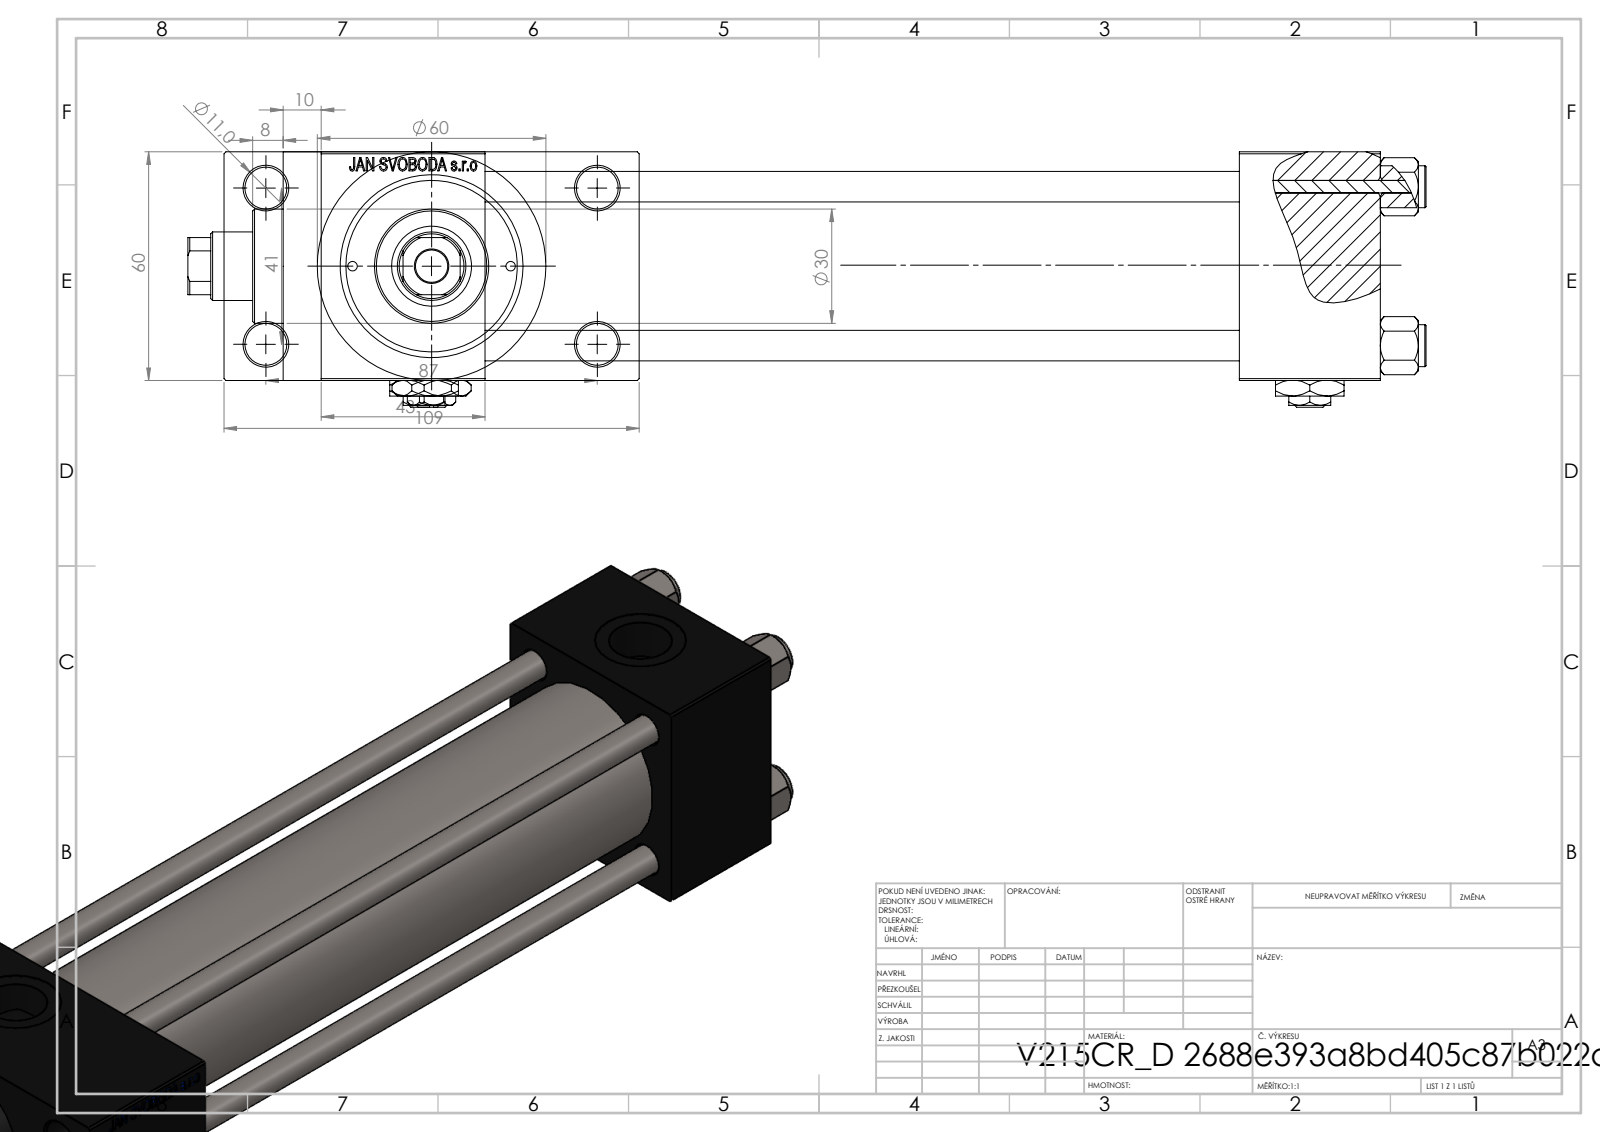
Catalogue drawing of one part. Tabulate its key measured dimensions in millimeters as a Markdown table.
| quantity | value |
| --- | --- |
| part name | V215CR_VCP_D; V215CR_D_Body; V215_VC_A; V215CR_D_TYCINKA (+2 more) |
| STEP written by | SolidWorks 2019 (CONFIG_CONTROL_DESIGN) |
| units | millimeters |
| bodies | 13 solids, 1214 faces (548 planar, 104 cylindrical, 562 other) |
| overall size | 325 × 109 × 67 |
| volume | 635 892 mm³ |
| surface area | 183 688 mm² |
| round holes (diameter × count) | 8 × 4, 11 × 4, 2.5 × 2, 7 × 2, 16.66 × 2, 24 × 2, 8.5 × 1, 18 × 1, 21 × 1, 31 × 1, 40 × 1, 45 × 1 |
| round bosses / shafts (diameter × count) | 11 × 4, 60 × 1, 46 × 1, 30 × 1 |
| partial cylindrical surfaces (radius × count) | 8.5 × 1 |
| main face-to-face distances | 60, 24.5, 84.5, 198, 37, 235, 43, 278, 241, 109 |
| hole center spacings | 20.85, 22.65, 29.49, 30.62, 41.7, 46.53, 47.15, 48.09 |
